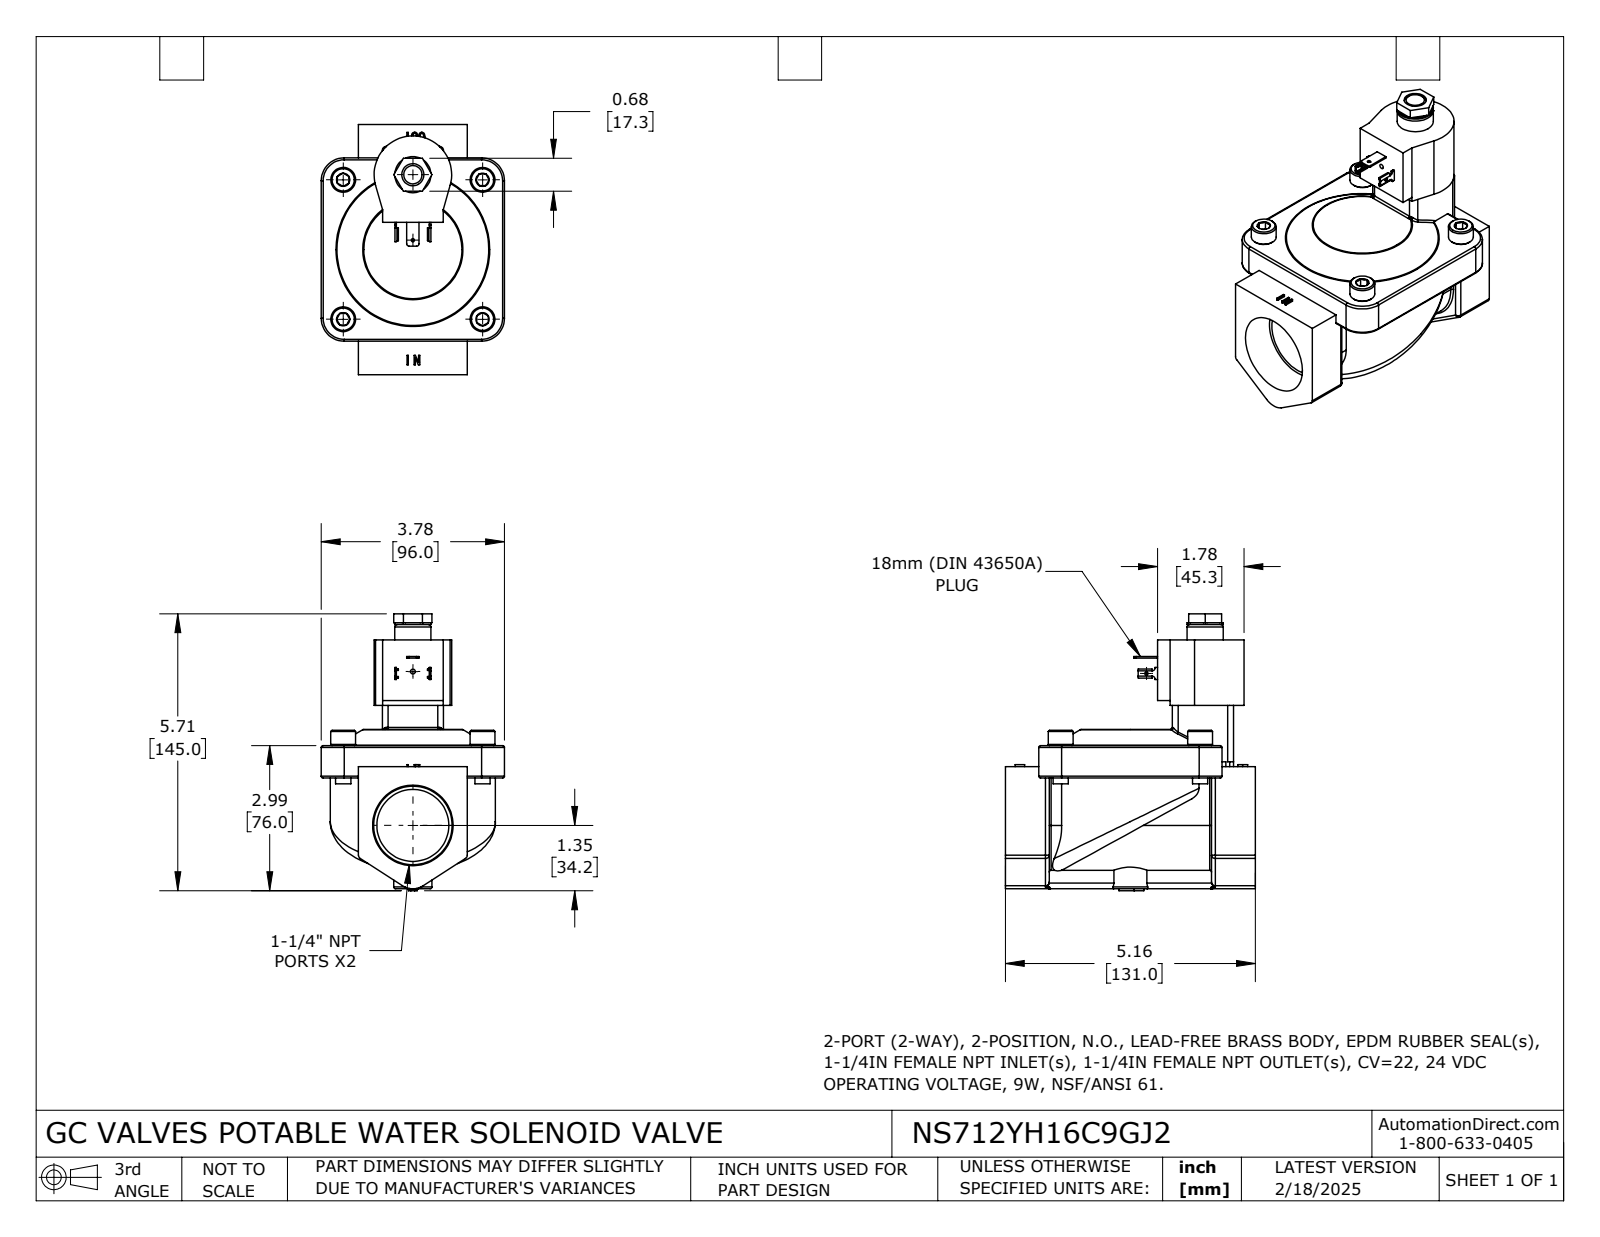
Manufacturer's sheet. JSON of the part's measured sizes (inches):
{"part_name": "NS712YH16C9GJ2", "step_written_by": "SolidWorks 2024 (CONFIG_CONTROL_DESIGN)", "units": "inches", "bodies": {"solids": 1, "faces": 456, "planar": 206, "cylindrical": 120, "other": 130}, "overall_size": [5.709, 5.157, 3.78], "volume_in3": 34.73, "surface_area_in2": 109.6, "round_holes": [[0.066, 1], [0.067, 1], [0.1, 1], [0.456, 1], [1.2, 1], [1.484, 1]], "round_bosses_or_shafts": [[0.512, 4], [0.315, 4], [0.746, 1]], "partial_cylinders_radius": [[0.079, 14], [0.039, 13], [0.118, 6], [0.006, 4], [0.041, 4], [0.472, 4], [0.008, 2], [0.05, 2]], "face_to_face_distances": [0.768, 0.433, 1.26, 0.236, 3.012, 0.335, 3.78, 0.669, 1.004, 2.244], "hole_center_spacings": [1.35, 3.172]}
